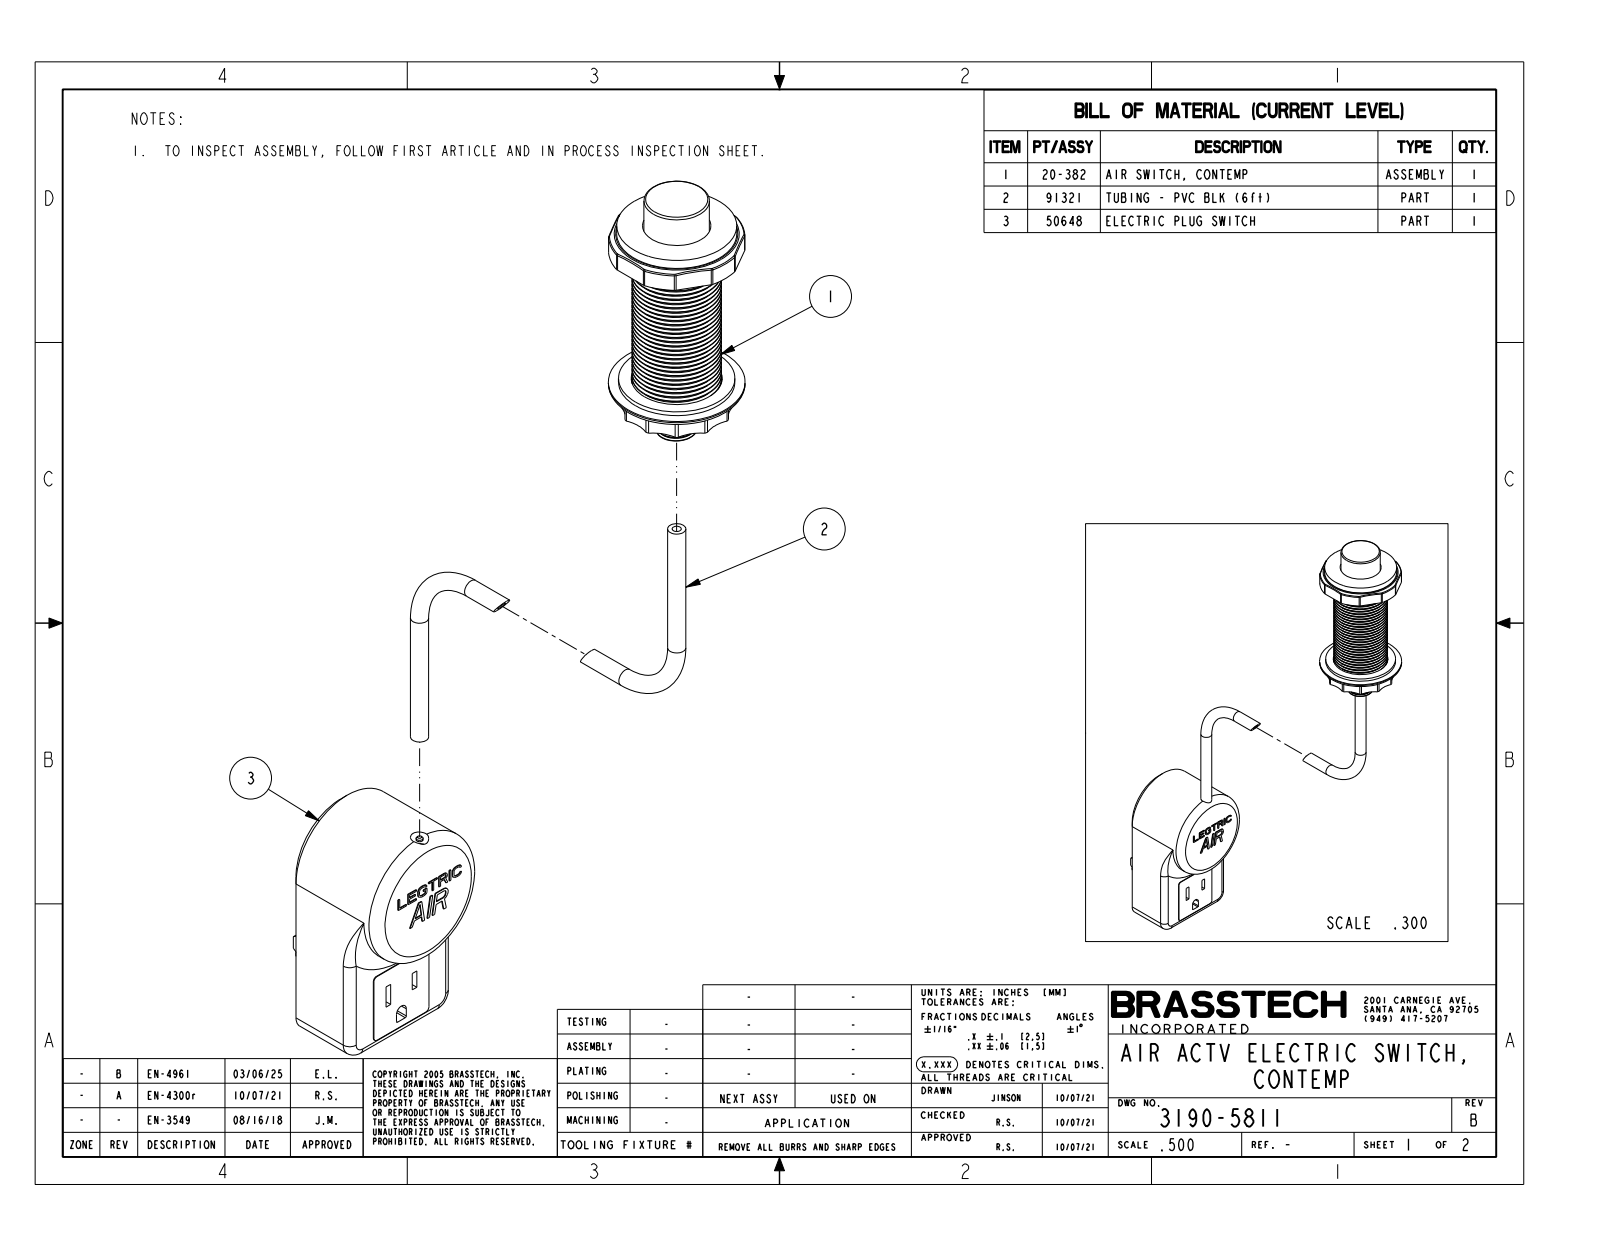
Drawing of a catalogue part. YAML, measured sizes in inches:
part_name: "3190-5811"
step_written_by: "CREO PARAMETRIC BY PTC INC, 2018400 (AUTOMOTIVE_DESIGN)"
units: inches
bodies: {solids: 3, faces: 517, planar: 260, cylindrical: 167, other: 90}
overall_size: [12.984, 8.313, 1.99]
volume: 14.22
surface_area: 68.4
round_holes:
  - {diameter: 0.125, count: 4}
  - {diameter: 0.94, count: 1}
  - {diameter: 1.25, count: 1}
round_bosses_or_shafts:
  - {diameter: 0.25, count: 3}
  - {diameter: 1.99, count: 1}
  - {diameter: 1.88, count: 1}
  - {diameter: 1.65, count: 1}
  - {diameter: 1.6, count: 1}
  - {diameter: 1.23, count: 1}
  - {diameter: 1.153, count: 1}
  - {diameter: 1.135, count: 1}
partial_cylinders:
  - {radius: 0.08, count: 12}
  - {radius: 0.5, count: 12}
  - {radius: 0.06, count: 4}
  - {radius: 0.125, count: 3}
  - {radius: 0.02, count: 2}
  - {radius: 0.25, count: 2}
  - {radius: 0.095, count: 1}
  - {radius: 0.81, count: 1}
face_to_face_distances: [1.99, 1.7, 0.08, 0.425, 0.36, 12.059, 12.484, 0.52, 1.18, 0.44]
hole_center_spacings: [5]
